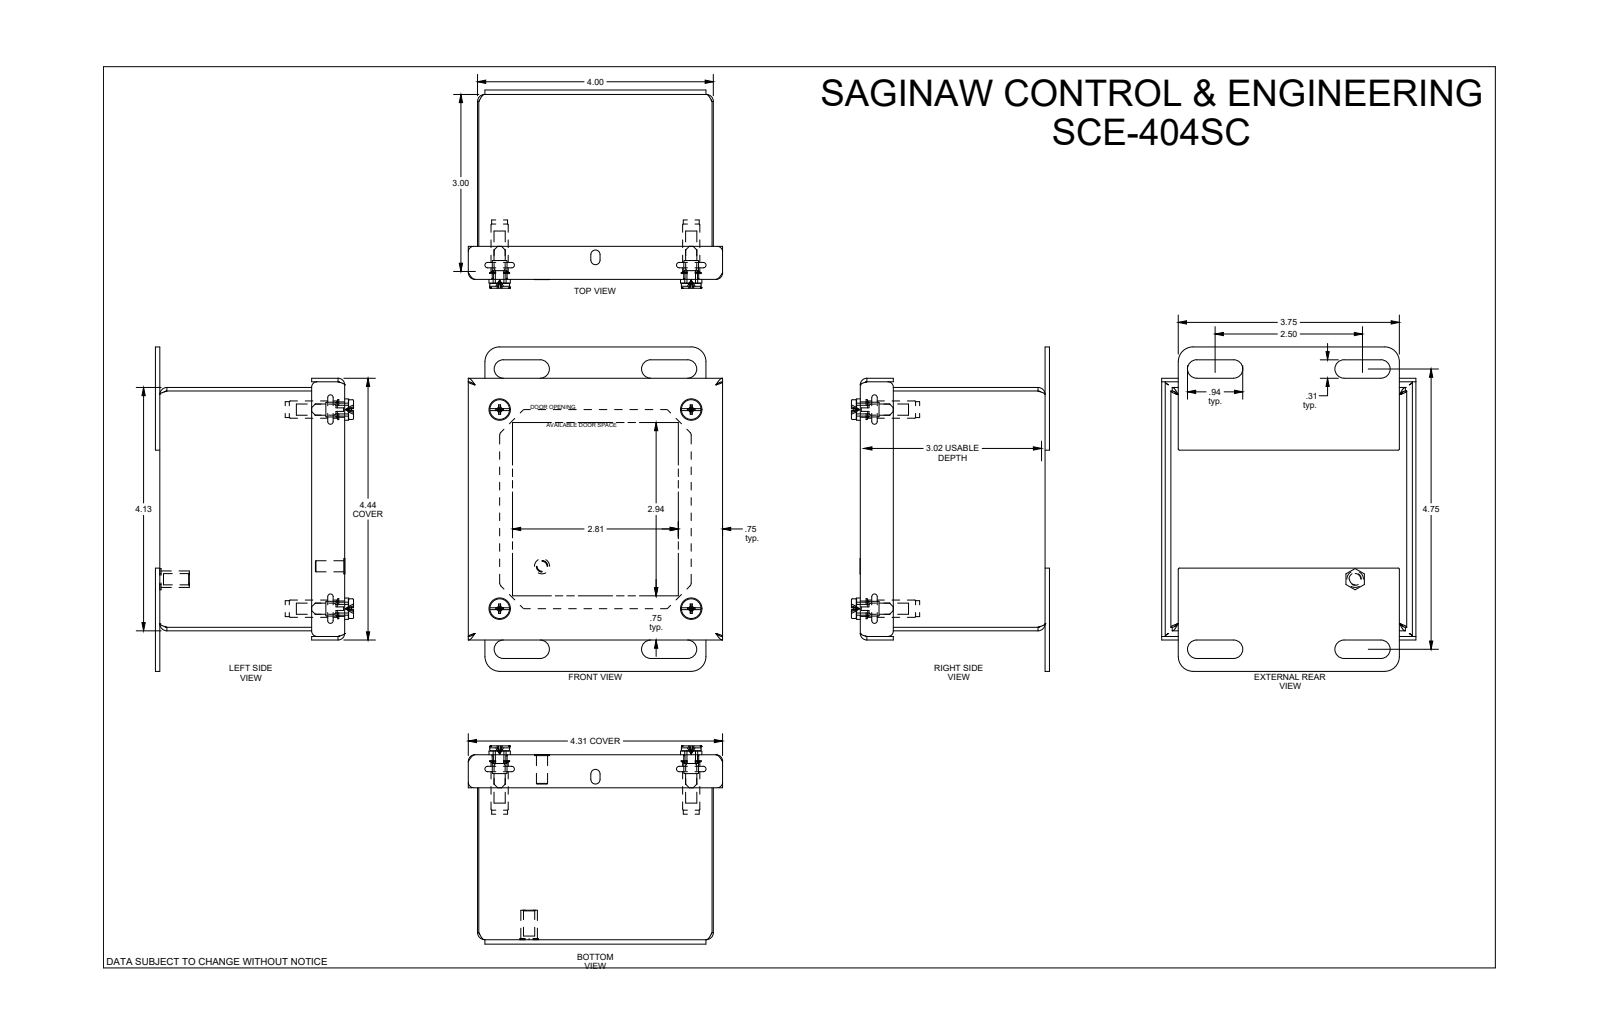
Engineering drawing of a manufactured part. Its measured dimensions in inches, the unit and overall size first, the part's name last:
Units: inches
Overall size (bounding box): 5.5 × 4.313 × 3.361
Round holes (diameter × count): ⌀0.19 ×4, ⌀0.22 ×4, ⌀0.25 ×4, ⌀0.266 ×4, ⌀0.281 ×4, ⌀0.317 ×4, ⌀0.187 ×1, ⌀0.193 ×1
Round bosses / shafts (diameter × count): ⌀0.188 ×5, ⌀0.437 ×4, ⌀0.362 ×4, ⌀0.34 ×4, ⌀0.334 ×4, ⌀0.292 ×4, ⌀0.27 ×4, ⌀0.26 ×4
Partial cylindrical surfaces — rounded edges, fillets, slot ends (radius × count): R0.06 ×12, R0.005 ×8, R0.05 ×8, R0.063 ×8, R0.125 ×8, R0.156 ×8, R0.255 ×8, R0.02 ×4
Main face-to-face distances: 0.06, 3.075, 3.94, 4.065, 3.135, 3.015, 0.156, 0.075, 0.135, 3.15
Hole centre spacings: 4.685, 0.752, 2.807, 3.25, 3.934, 3.375, 2.857, 2.857
Volume: 7.24 in³ · Surface area: 239.1 in²
Bodies: 18 solids, 509 faces (195 planar, 149 cylindrical, 165 other)
Part name (STEP PRODUCT): SCE-404SC
STEP written by: SolidWorks 2021 (AUTOMOTIVE_DESIGN)
